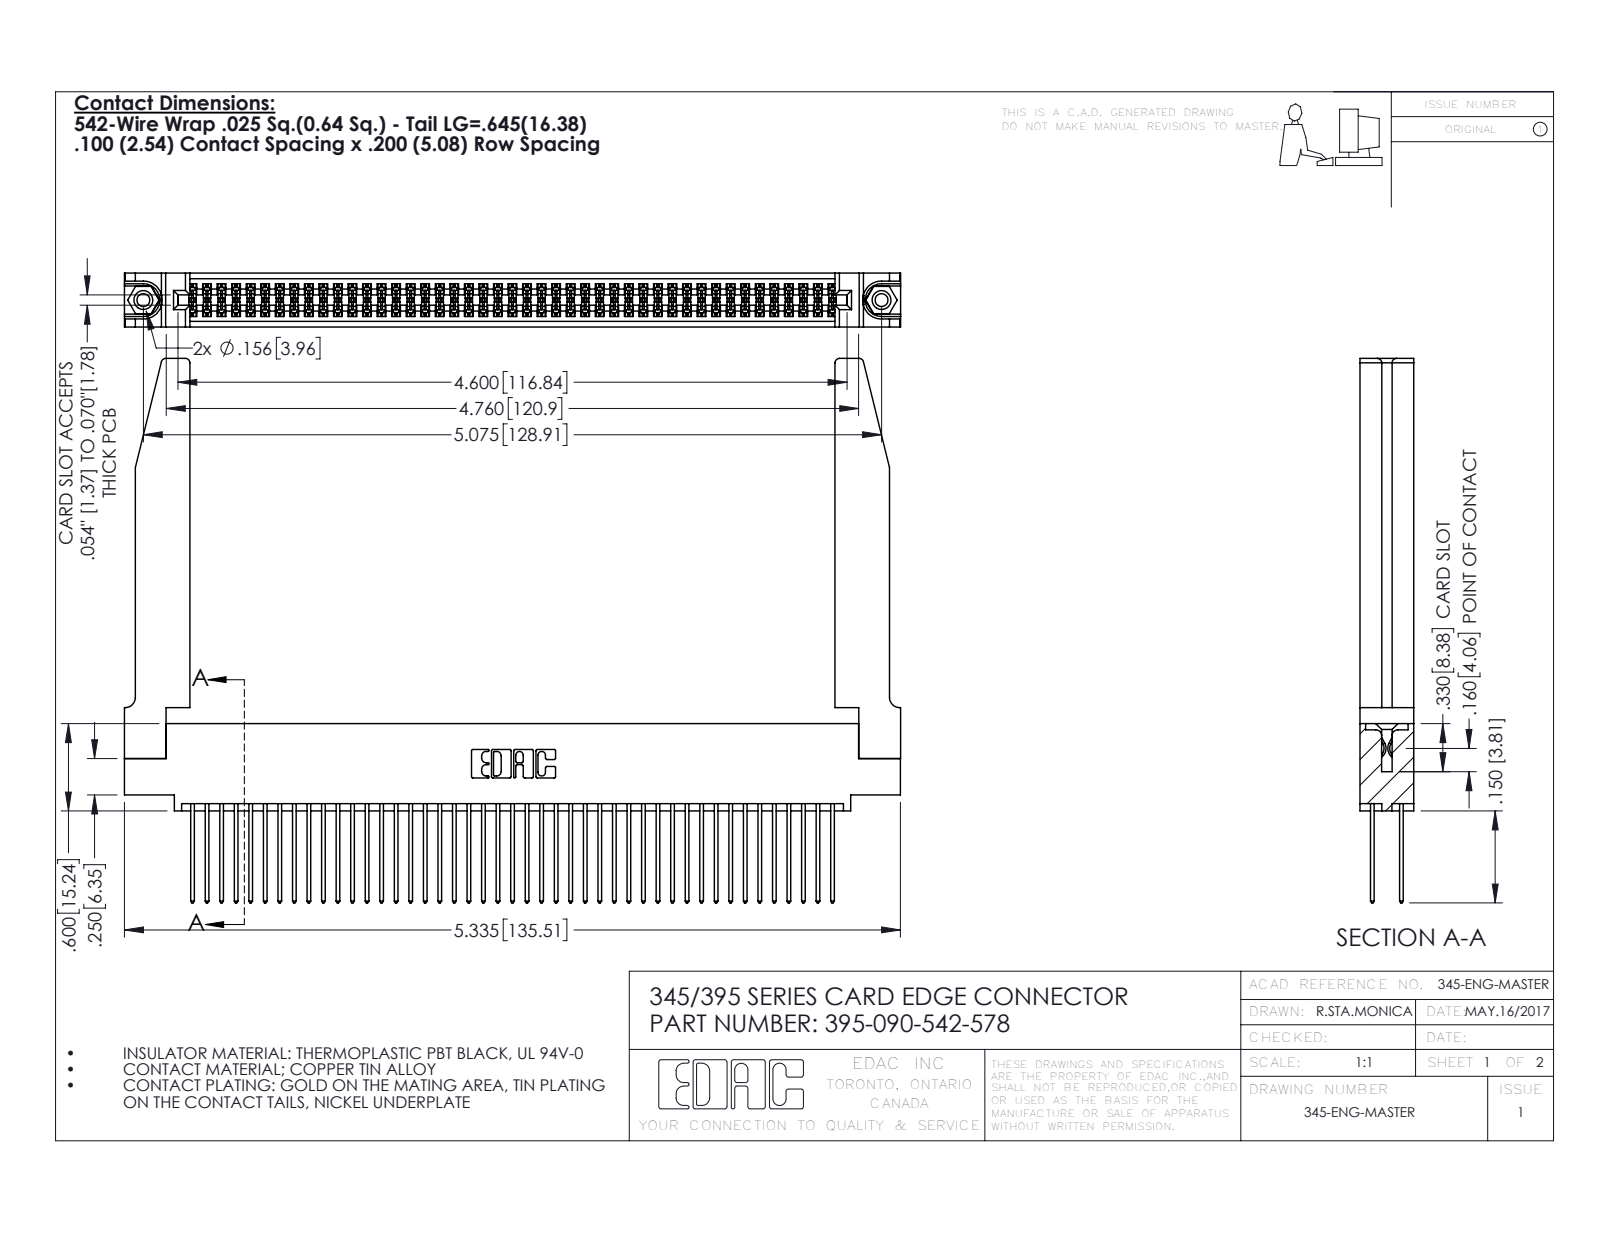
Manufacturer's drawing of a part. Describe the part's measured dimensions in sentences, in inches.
The part is named "345-250-001_345-250-001-102; 345 Part_0.110 Offset - 0.156 Dia-TH; 345-292-001_345-293-142; 395-090-542-578 (+1 more)". Its 3-D file was written by "SolidWorks 2016 (CONFIG_CONTROL_DESIGN)". It is 95 solids with 4864 faces: 3196 planar, 1616 cylindrical and 52 other. Overall it measures 5.336 by 3.742 by 0.37 inches. Its volume is 1.3 cubic inches and its surface area 44.89 square inches. Round holes: 2 of diameter 0.089, 2 of diameter 0.125, 2 of diameter 0.156, 1 of diameter 0.064. Round bosses or shafts: 2 of diameter 0.155. Partial cylindrical surfaces (rounded edges, fillets, slot ends): 135 of radius 0.006, 90 of radius 0.01, 22 of radius 0.01, 8 of radius 0.03, 6 of radius 0.007, 6 of radius 0.031, 3 of radius 0.026, 2 of radius 0.014. The main face-to-face distances are 0.072, 0.298, 0.37, 0.2, 0.098, 0.272, 0.025, 0.225, 0.175, 0.148. The hole center spacings are 0.27, 4.839, 5.075.
